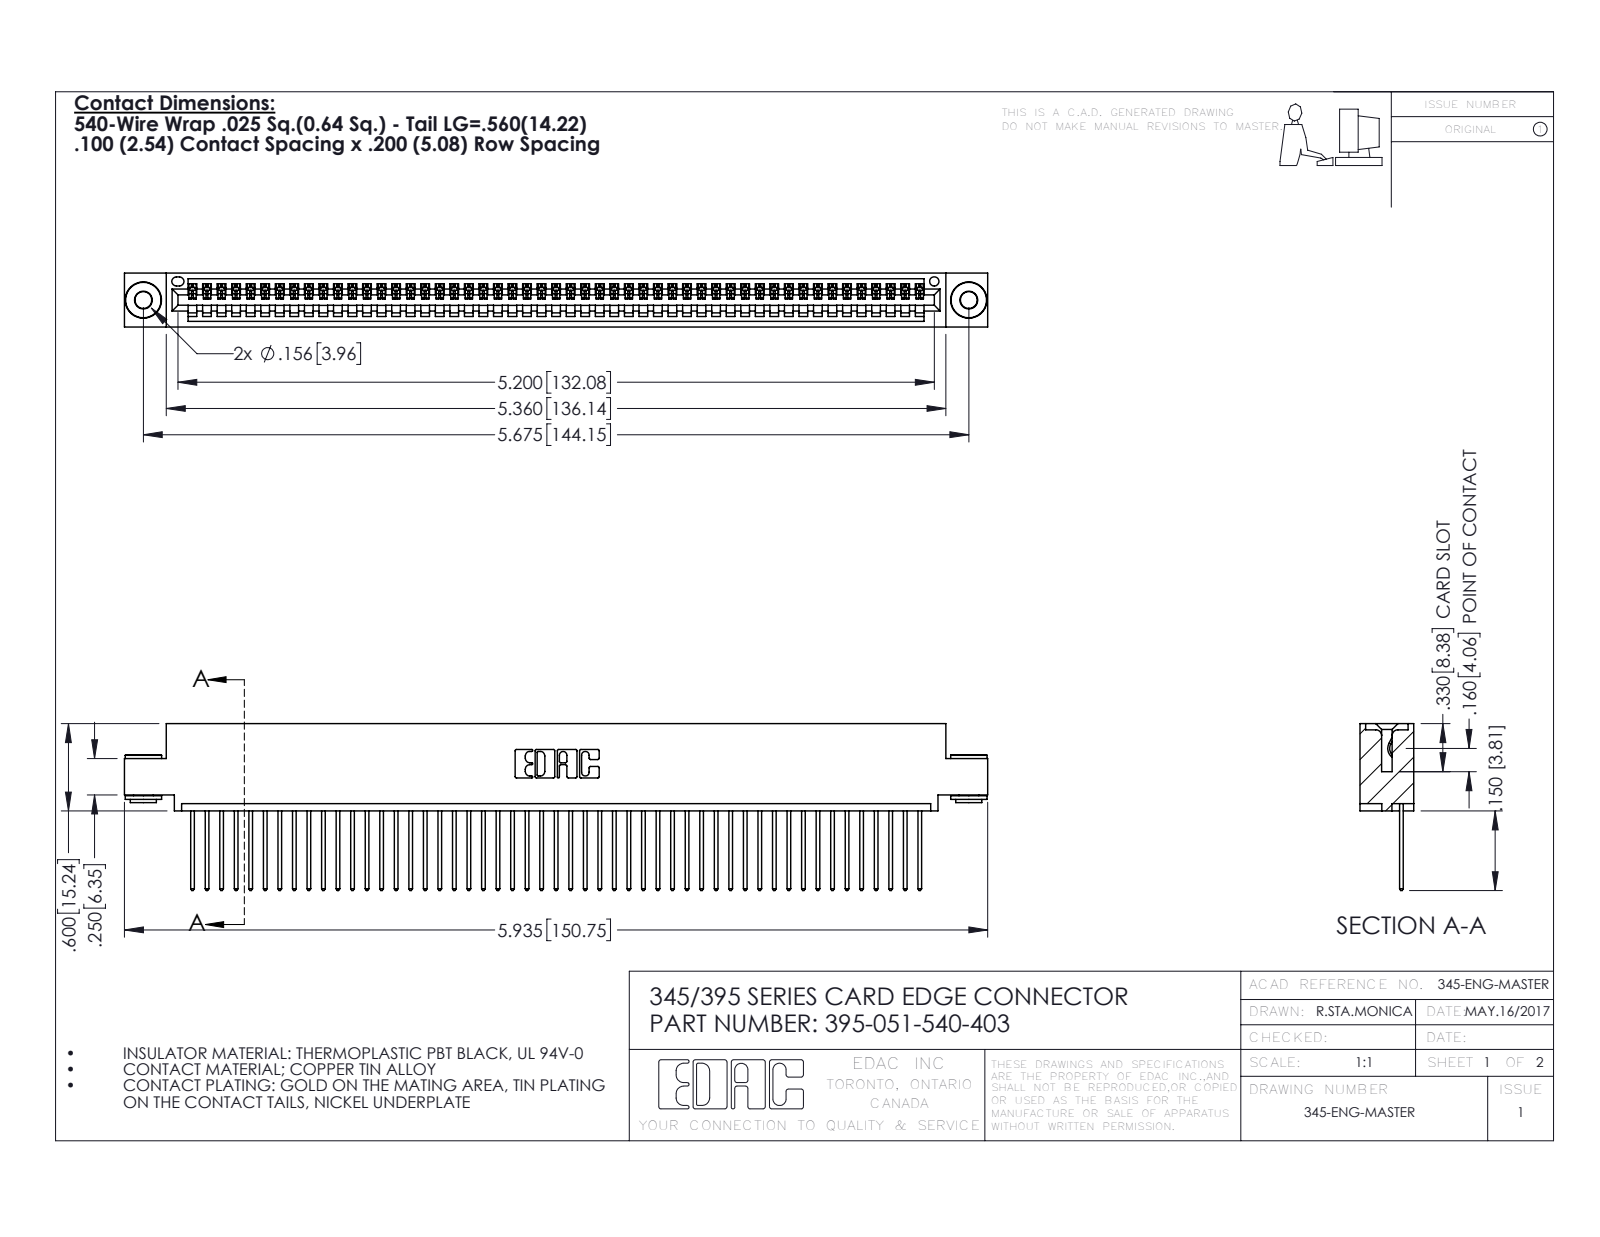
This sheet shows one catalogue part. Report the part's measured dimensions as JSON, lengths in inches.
{"part_name": "345-250-002_345-250-002-102; 345 Part_0.110 Offset - 0.156 Dia-TH; 395-051-540-403; 345-292-001_345-293-140", "step_written_by": "SolidWorks 2016 (CONFIG_CONTROL_DESIGN)", "units": "inches", "bodies": {"solids": 54, "faces": 3126, "planar": 2134, "cylindrical": 984, "other": 8}, "overall_size": [5.935, 1.147, 0.37], "volume_in3": 0.879, "surface_area_in2": 31.1, "round_holes": [[0.116, 2], [0.156, 2], [0.064, 1]], "round_bosses_or_shafts": [[0.25, 2], [0.18, 2], [0.136, 2]], "partial_cylinders_radius": [[0.006, 102], [0.01, 102], [0.01, 22], [0.007, 6], [0.031, 6], [0.026, 3], [0.031, 2], [0.04, 2]], "face_to_face_distances": [0.072, 0.298, 0.025, 0.37, 0.098, 0.272, 0.2, 0.225, 0.149, 0.072], "hole_center_spacings": [0.27, 5.439, 5.675]}
